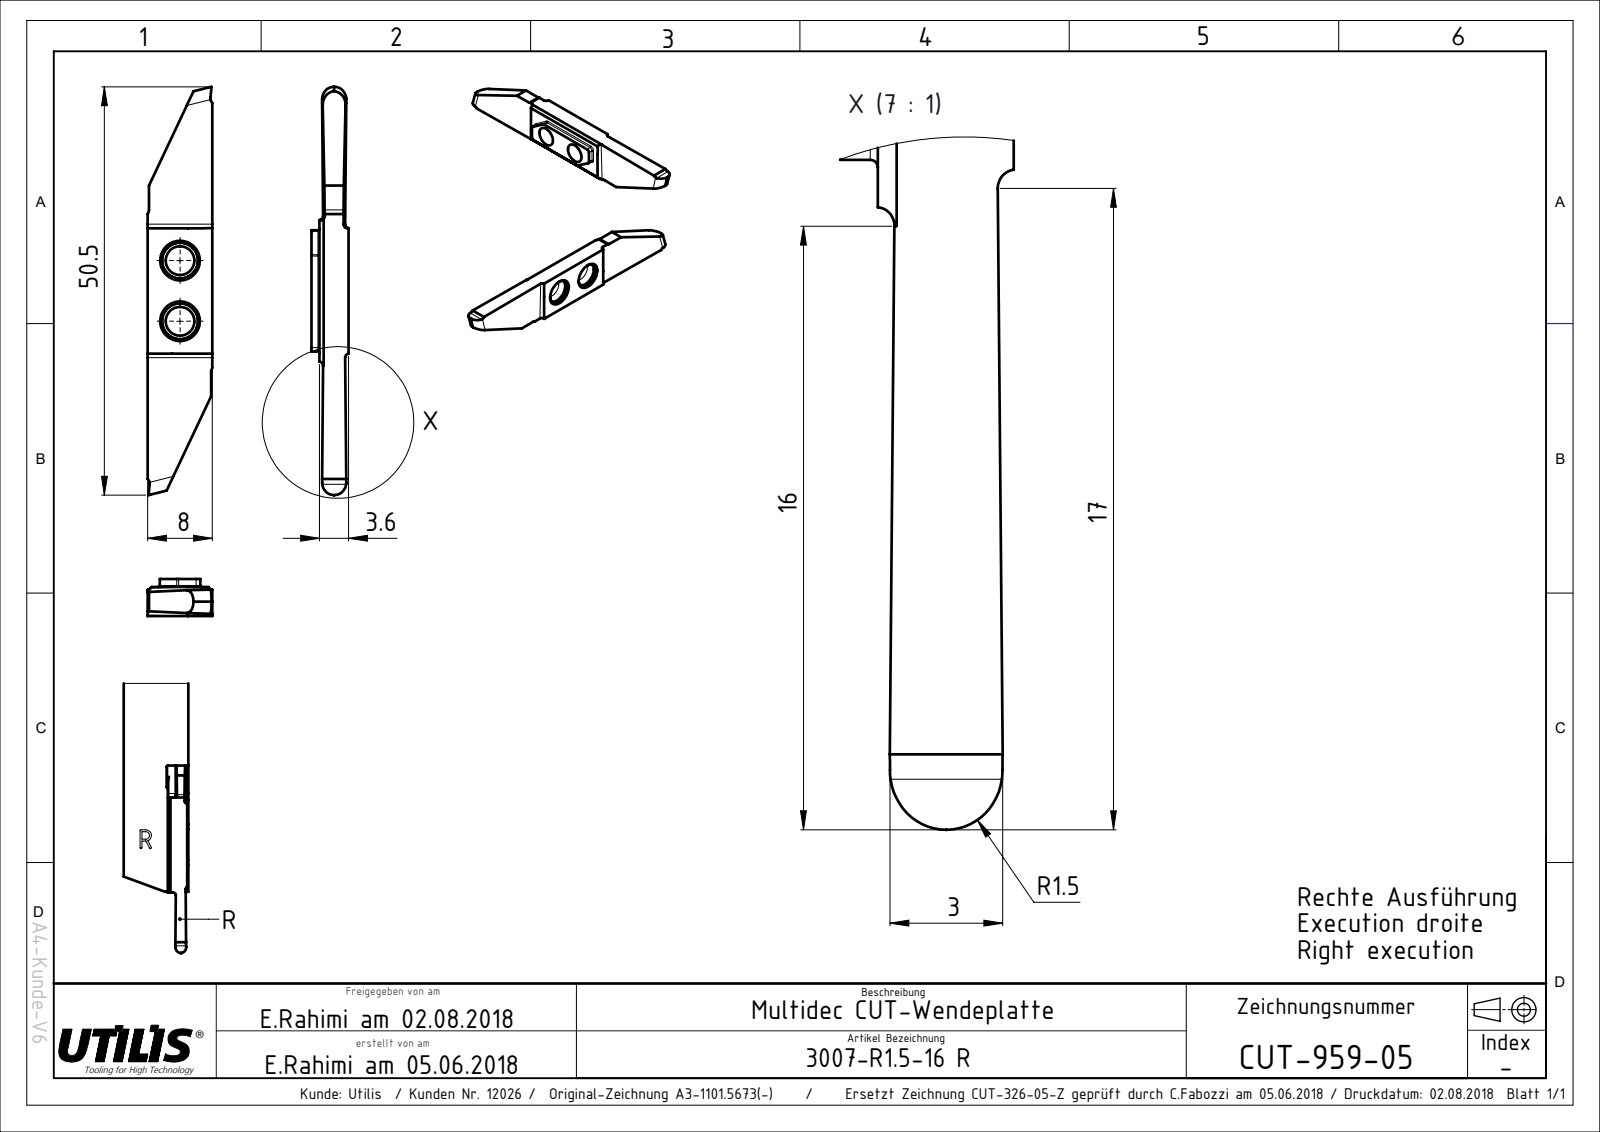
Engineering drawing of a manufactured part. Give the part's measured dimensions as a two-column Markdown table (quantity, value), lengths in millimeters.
| quantity | value |
| --- | --- |
| part name | CUT-959; ASME Y14.5 |
| STEP written by | FormatWorks Professional (AP242_MANAGED_MODEL_BASED_3D_ENGINEERING_MIM_LF) |
| units | millimeters |
| bodies | 1 solid, 40 faces (22 planar, 18 cylindrical, 0 other) |
| overall size | 50.5 × 8 × 3.6 |
| volume | 915 mm³ |
| surface area | 1 010 mm² |
| round holes (diameter × count) | 3.55 × 2 |
| partial cylindrical surfaces (radius × count) | 0.5 × 4, 1.5 × 4, 0.8 × 2, 1 × 2 |
| main face-to-face distances | 2.37, 8, 3.6, 18.09, 7.85, 7.7, 7, 15.5, 1.5, 17 |
| hole center spacings | 7.5 |
